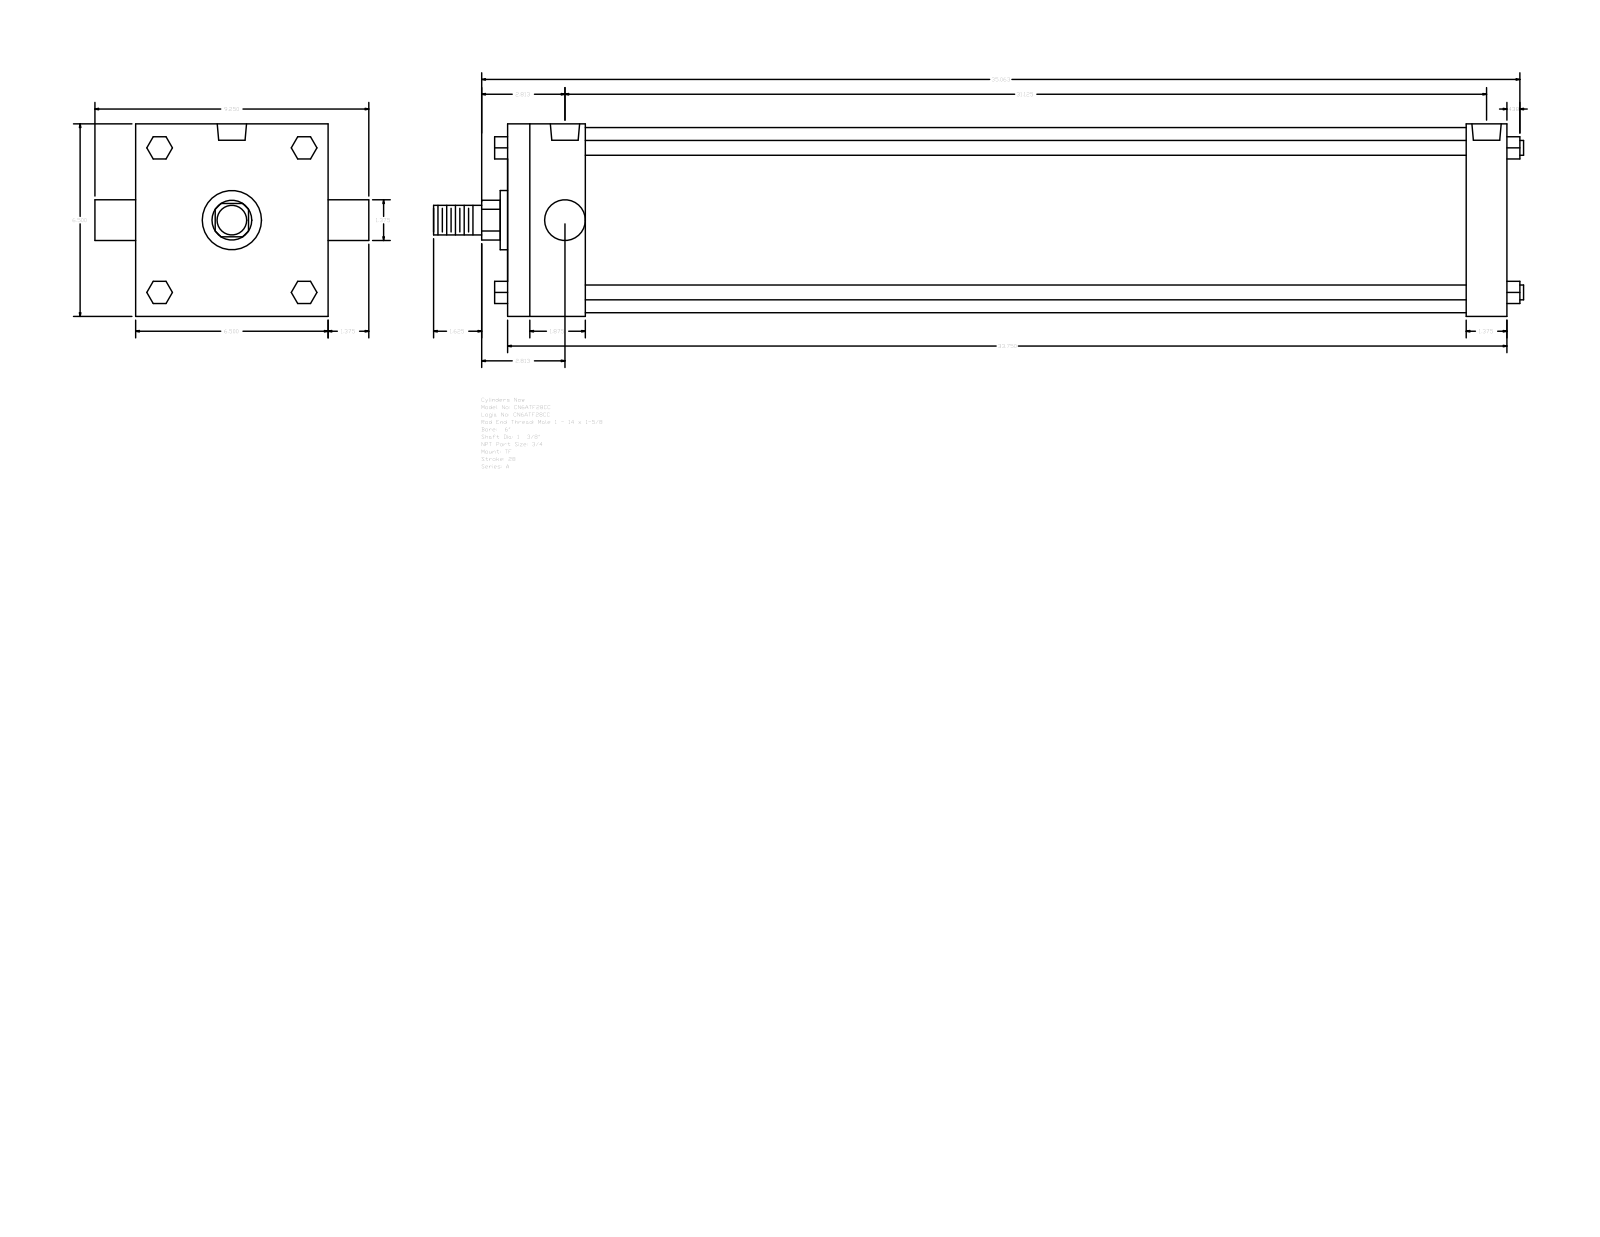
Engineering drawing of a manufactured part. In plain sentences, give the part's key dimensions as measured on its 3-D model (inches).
The part is named "A_TF__0600_1.375". Its 3-D file was written by "GSSL Pune (CONFIG_CONTROL_DESIGN)". It is 0 solids with 120 faces: 92 planar, 28 cylindrical and 0 other. Overall it measures 36.813 by 9.25 by 6.5 inches. Round holes: 3 of diameter 0.594, 2 of diameter 0.989. Round bosses or shafts: 4 of diameter 0.5, 2 of diameter 1.375, 1 of diameter 6.25, 1 of diameter 2, 1 of diameter 1. Partial cylindrical surfaces (rounded edges, fillets, slot ends): 1 of radius 0.672. The main face-to-face distances are 6.5, 33.75, 2.625, 31.125, 32.375, 29.75, 1.375, 0.75, 2.44, 4.226. The hole center spacings are 0.219, 30.906, 30.687, 31.125.
